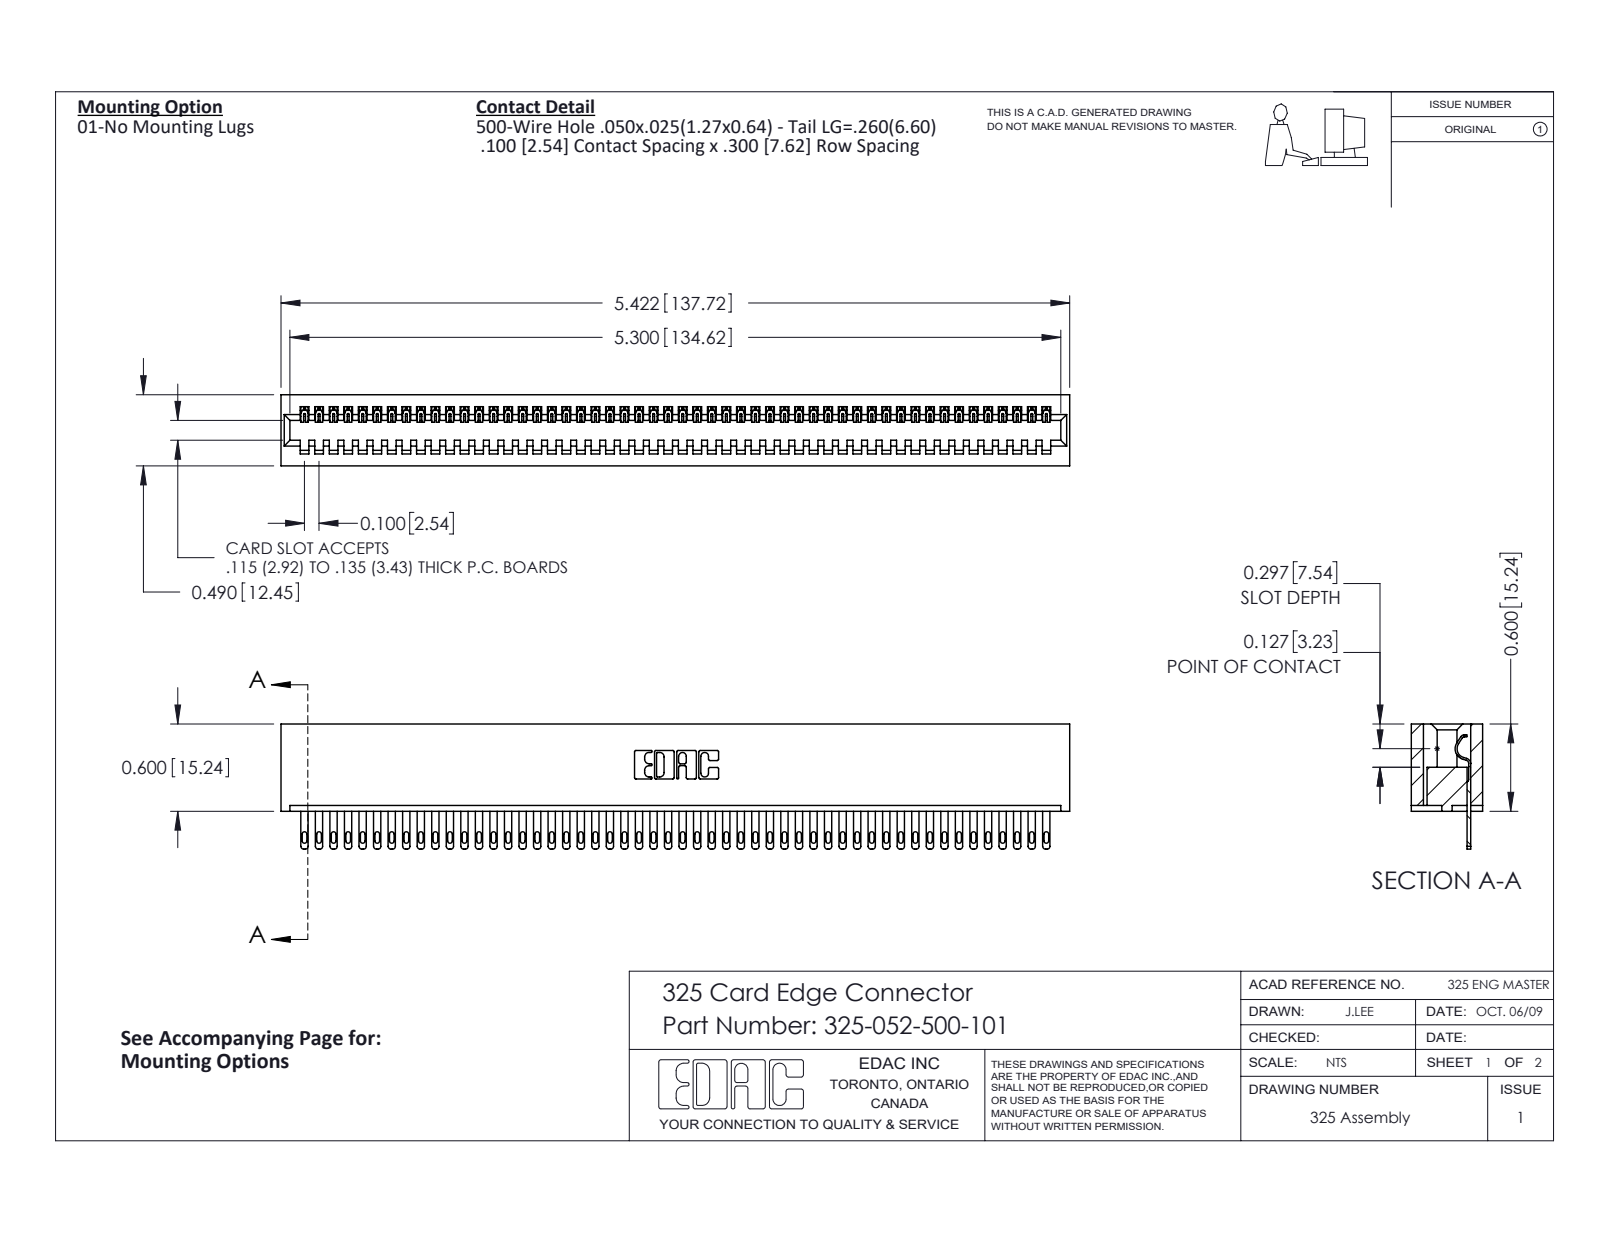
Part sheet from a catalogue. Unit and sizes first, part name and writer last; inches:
Units: inches
Overall size (bounding box): 5.422 × 0.86 × 0.49
Partial cylindrical surfaces — rounded edges, fillets, slot ends (radius × count): R0.006 ×104, R0.016 ×104, R0.02 ×104, R0.01 ×22, R0.007 ×6, R0.031 ×6, R0.026 ×3, R0.014 ×1
Main face-to-face distances: 0.083, 0.407, 0.3, 0.49, 0.107, 0.383, 0.025, 0.325, 0.56, 0.263
Volume: 1.109 in³ · Surface area: 31.97 in²
Bodies: 53 solids, 2914 faces (1938 planar, 976 cylindrical, 0 other)
Part name (STEP PRODUCT): 325 Part_Lugless; 325-052-500-101; 325-292-001_325-293-100
STEP written by: SolidWorks 2016 (CONFIG_CONTROL_DESIGN)
